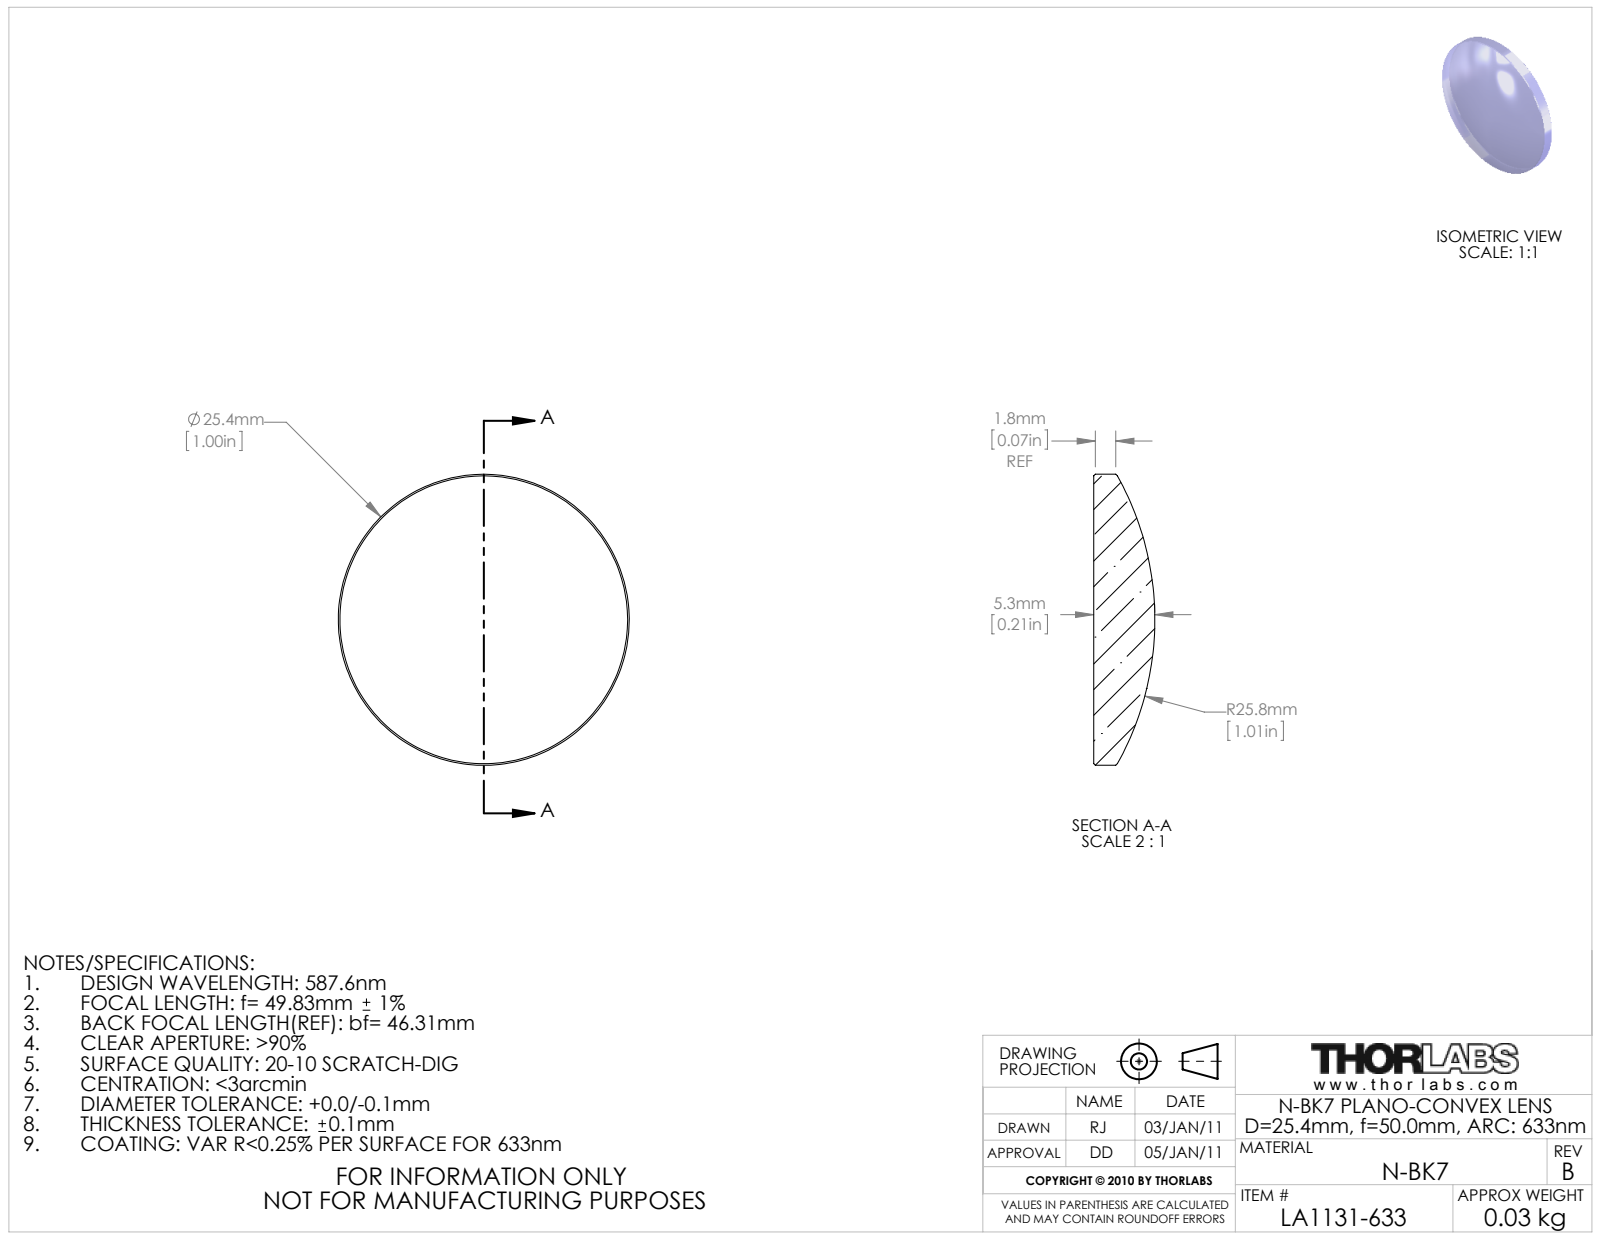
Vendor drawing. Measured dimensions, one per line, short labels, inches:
name: 21786-E0W
written by: SolidWorks 2011 (AUTOMOTIVE_DESIGN)
unit: in
bodies: 0 solids, 9 faces (1 planar, 2 cylindrical, 6 other)
size: 1 × 1 × 0.21
bosses: 1× ⌀1
